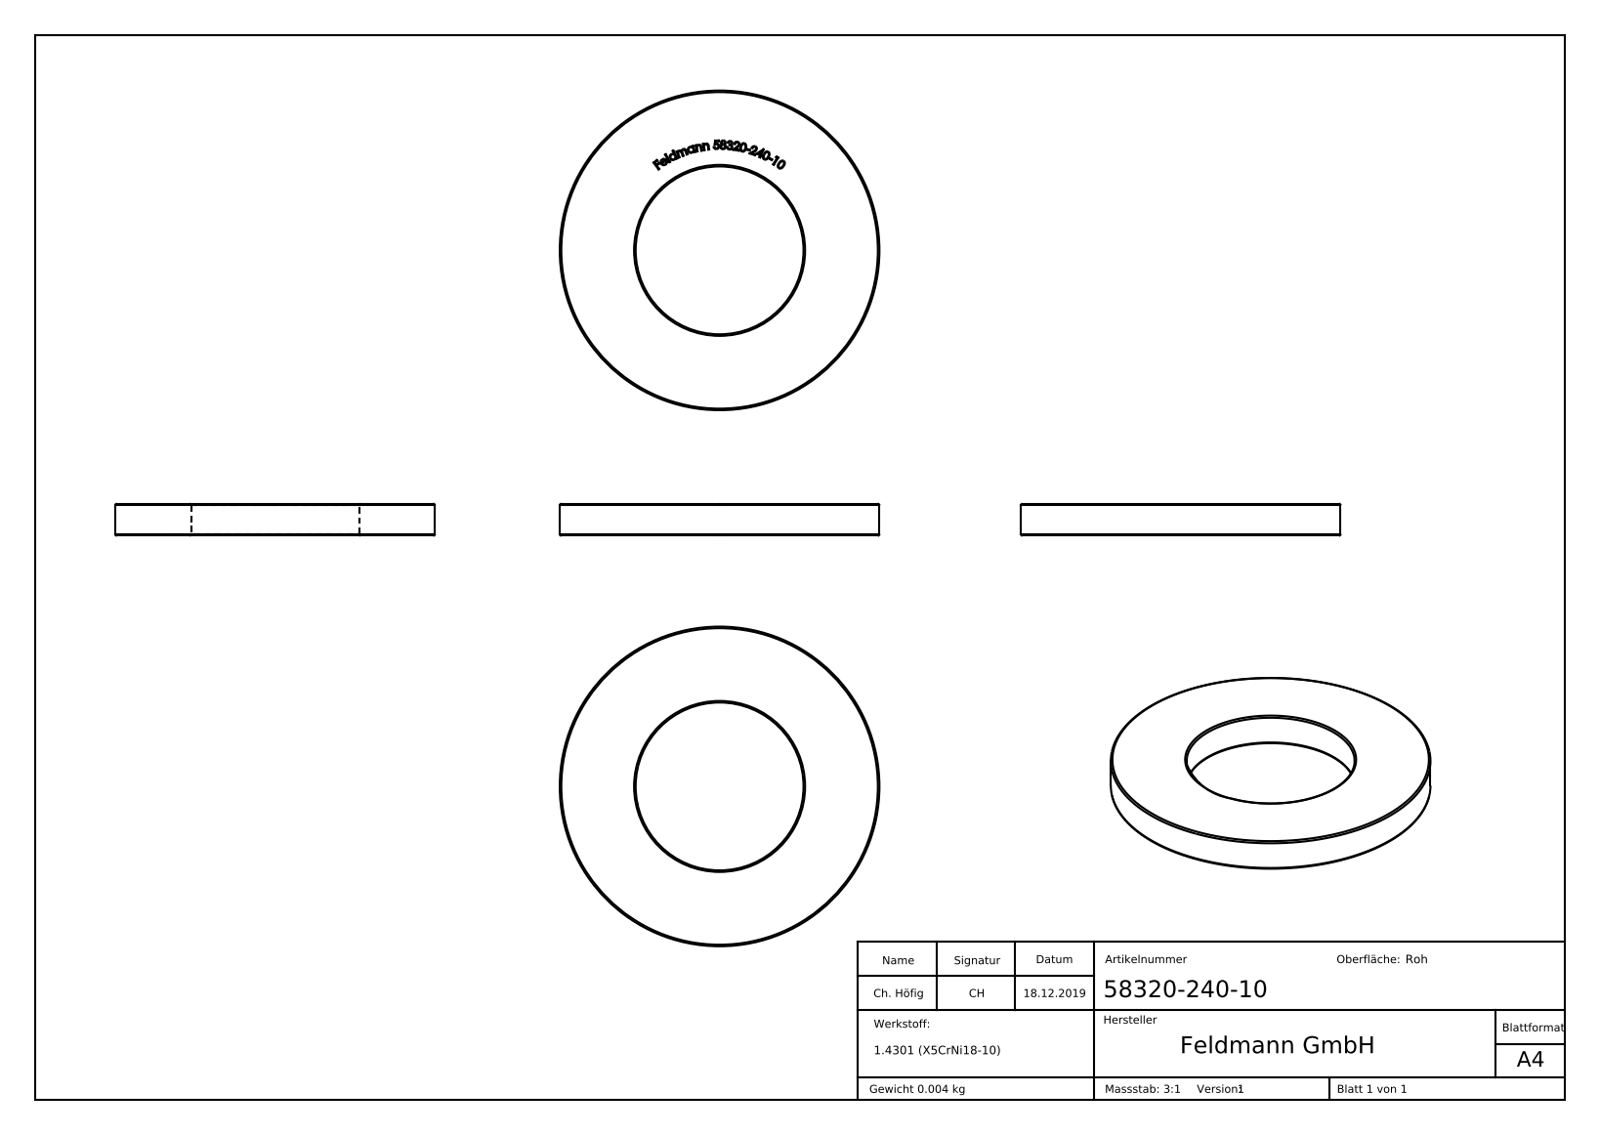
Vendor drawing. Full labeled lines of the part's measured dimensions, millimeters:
Part name (STEP PRODUCT): 58320-240-10
STEP written by: SolidWorks 2015 (CONFIG_CONTROL_DESIGN)
Units: millimetres
Bodies: 1 solid, 265 faces (133 planar, 2 cylindrical, 130 other)
Overall size (bounding box): 20 × 20 × 2
Volume: 455 mm³ · Surface area: 643 mm²
Round holes (diameter × count): ⌀10.5 ×1
Round bosses / shafts (diameter × count): ⌀20 ×1
Main face-to-face distances: 2, 1.9, 0.34, 0.53, 0.58, 0.31, 0.32, 0.39, 0.48, 0.54
